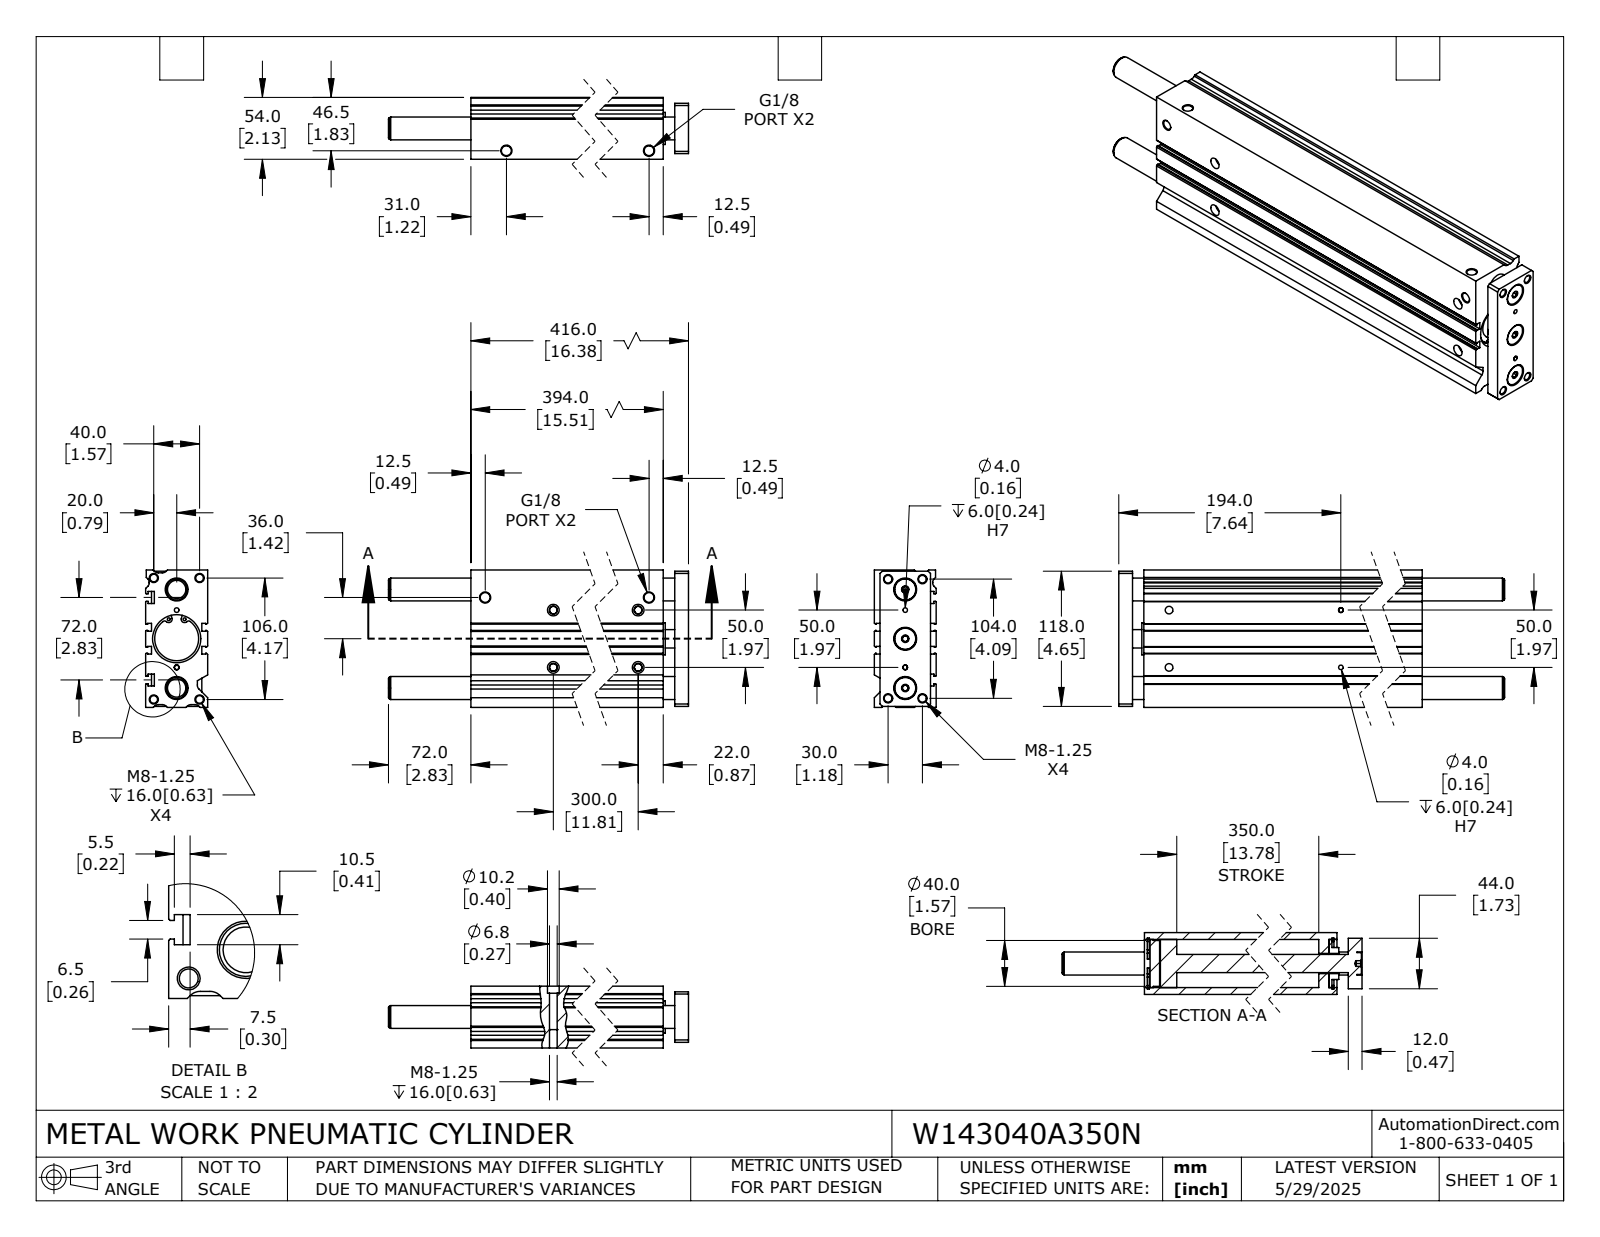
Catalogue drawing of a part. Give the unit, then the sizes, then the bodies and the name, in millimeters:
Units: millimetres
Overall size (bounding box): 488 × 120 × 54
Round holes (diameter × count): ⌀6.7 ×10, ⌀2.5 ×4, ⌀4 ×4, ⌀6.8 ×4, ⌀8.6 ×4, ⌀10.2 ×4, ⌀5 ×3, ⌀20 ×3, ⌀6.7 ×2, ⌀17.7 ×1, ⌀38.4 ×1
Round bosses / shafts (diameter × count): ⌀19 ×3, ⌀44.5 ×2, ⌀42 ×1, ⌀40 ×1, ⌀28 ×1, ⌀16 ×1
Partial cylindrical surfaces — rounded edges, fillets, slot ends (radius × count): R5 ×7, R2 ×4, R2.3 ×4, R2.9 ×4, R4 ×2
Main face-to-face distances: 54, 5, 49, 2.5, 120, 7.5, 46.5, 41.5, 44, 72
Hole centre spacings: 5.1, 10.5, 17.5, 18.3, 22.4, 26.9, 30.9, 34.4
Volume: 2 040 000 mm³ · Surface area: 407 600 mm²
Bodies: 6 solids, 393 faces (192 planar, 151 cylindrical, 50 other)
Part name (STEP PRODUCT): W143040A350N; W143040A350N_BODY; W143040A350N_ROD
STEP written by: SolidWorks 2024 (CONFIG_CONTROL_DESIGN)
